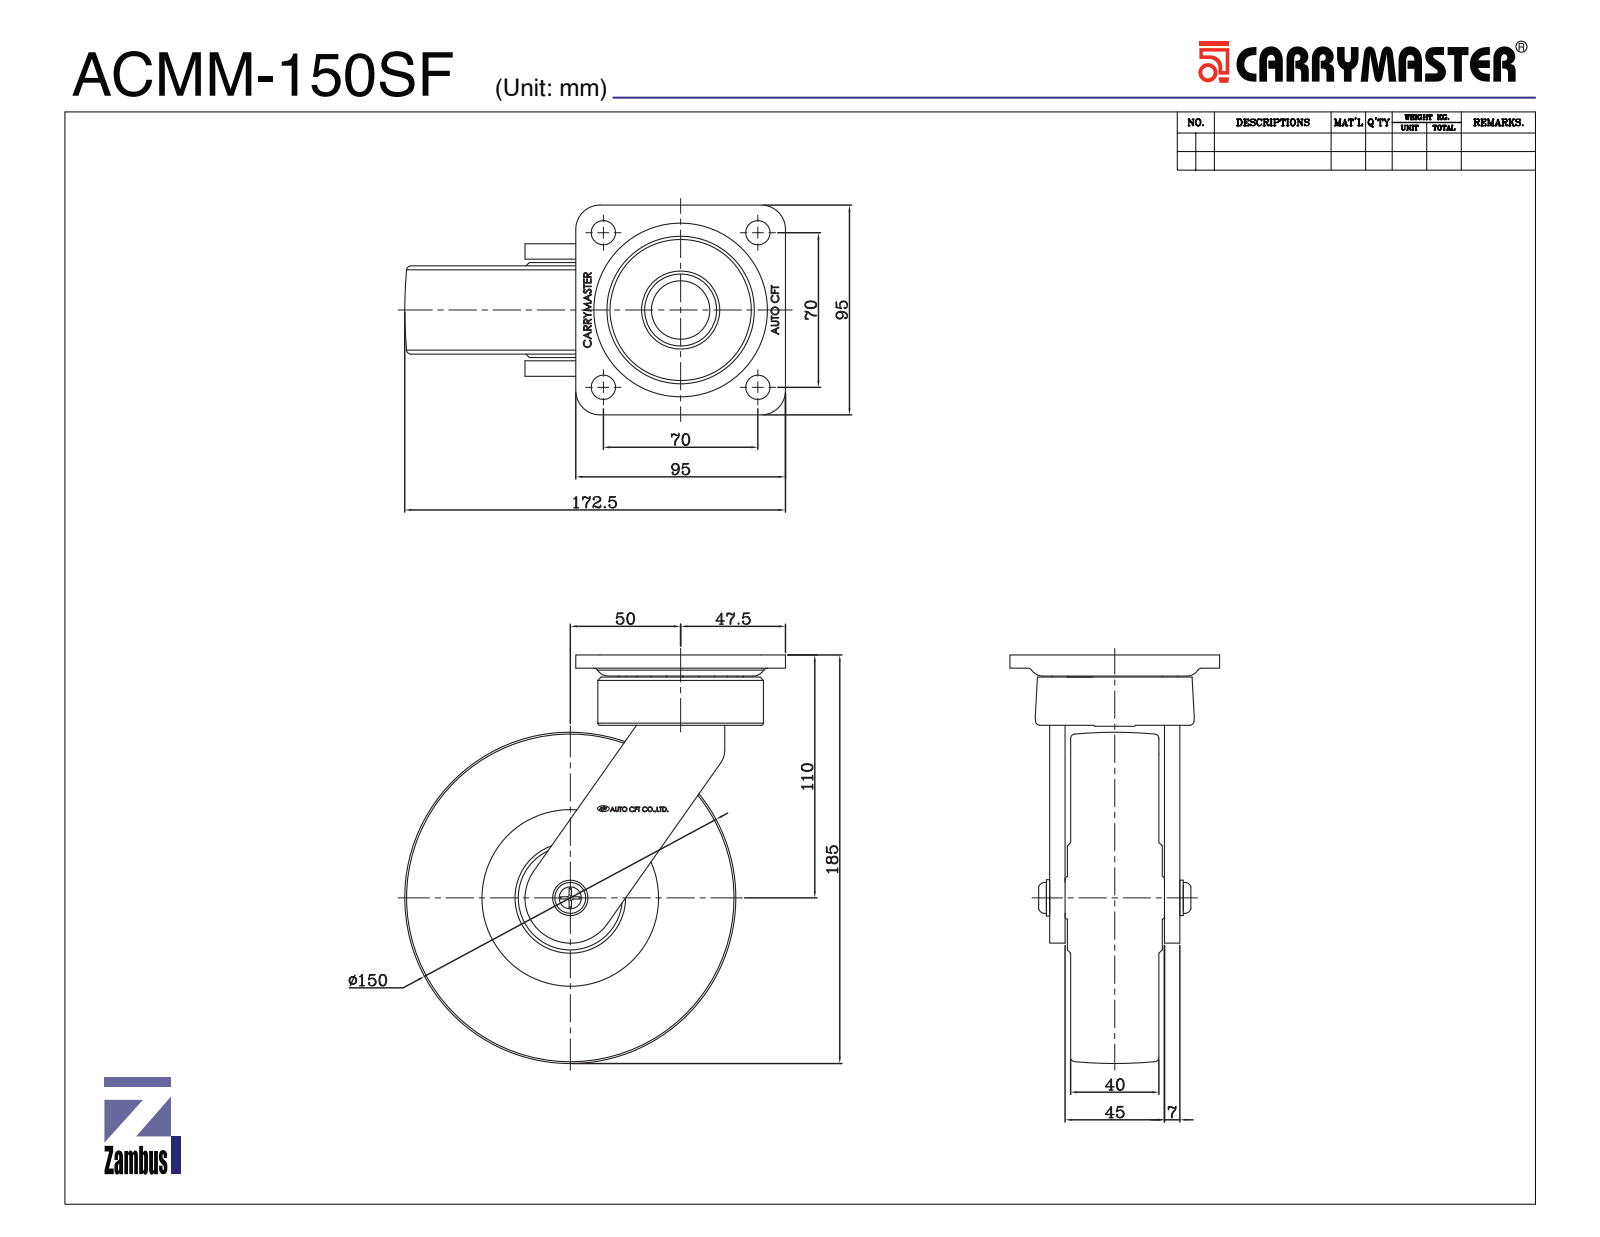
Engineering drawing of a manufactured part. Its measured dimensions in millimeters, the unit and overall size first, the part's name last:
Units: millimetres
Overall size (bounding box): 185 × 172.5 × 95
Round holes (diameter × count): ⌀11 ×4, ⌀6.8 ×1, ⌀12 ×1, ⌀12.3 ×1, ⌀17.5 ×1, ⌀19.63 ×1, ⌀22.54 ×1, ⌀26.5 ×1, ⌀29.94 ×1, ⌀31.1 ×1, ⌀42 ×1, ⌀62 ×1
Round bosses / shafts (diameter × count): ⌀38 ×1, ⌀37 ×1, ⌀26.46 ×1, ⌀25 ×1, ⌀20 ×1, ⌀19.06 ×1, ⌀16 ×1, ⌀14 ×1
Partial cylindrical surfaces — rounded edges, fillets, slot ends (radius × count): R2 ×12, R5 ×4, R11 ×4, R0.52 ×2, R12 ×1, R14.5 ×1, R18.3 ×1, R20 ×1
Main face-to-face distances: 40, 2.5, 9.5, 42.5, 7, 49.5, 52, 45, 6, 59
Hole centre spacings: 49.5, 70, 98.99
Volume: 876 185 mm³ · Surface area: 134 156 mm²
Bodies: 12 solids, 1314 faces (599 planar, 157 cylindrical, 558 other)
Part name (STEP PRODUCT): ACMM-150SF
STEP written by: SolidWorks 2015 (CONFIG_CONTROL_DESIGN)
